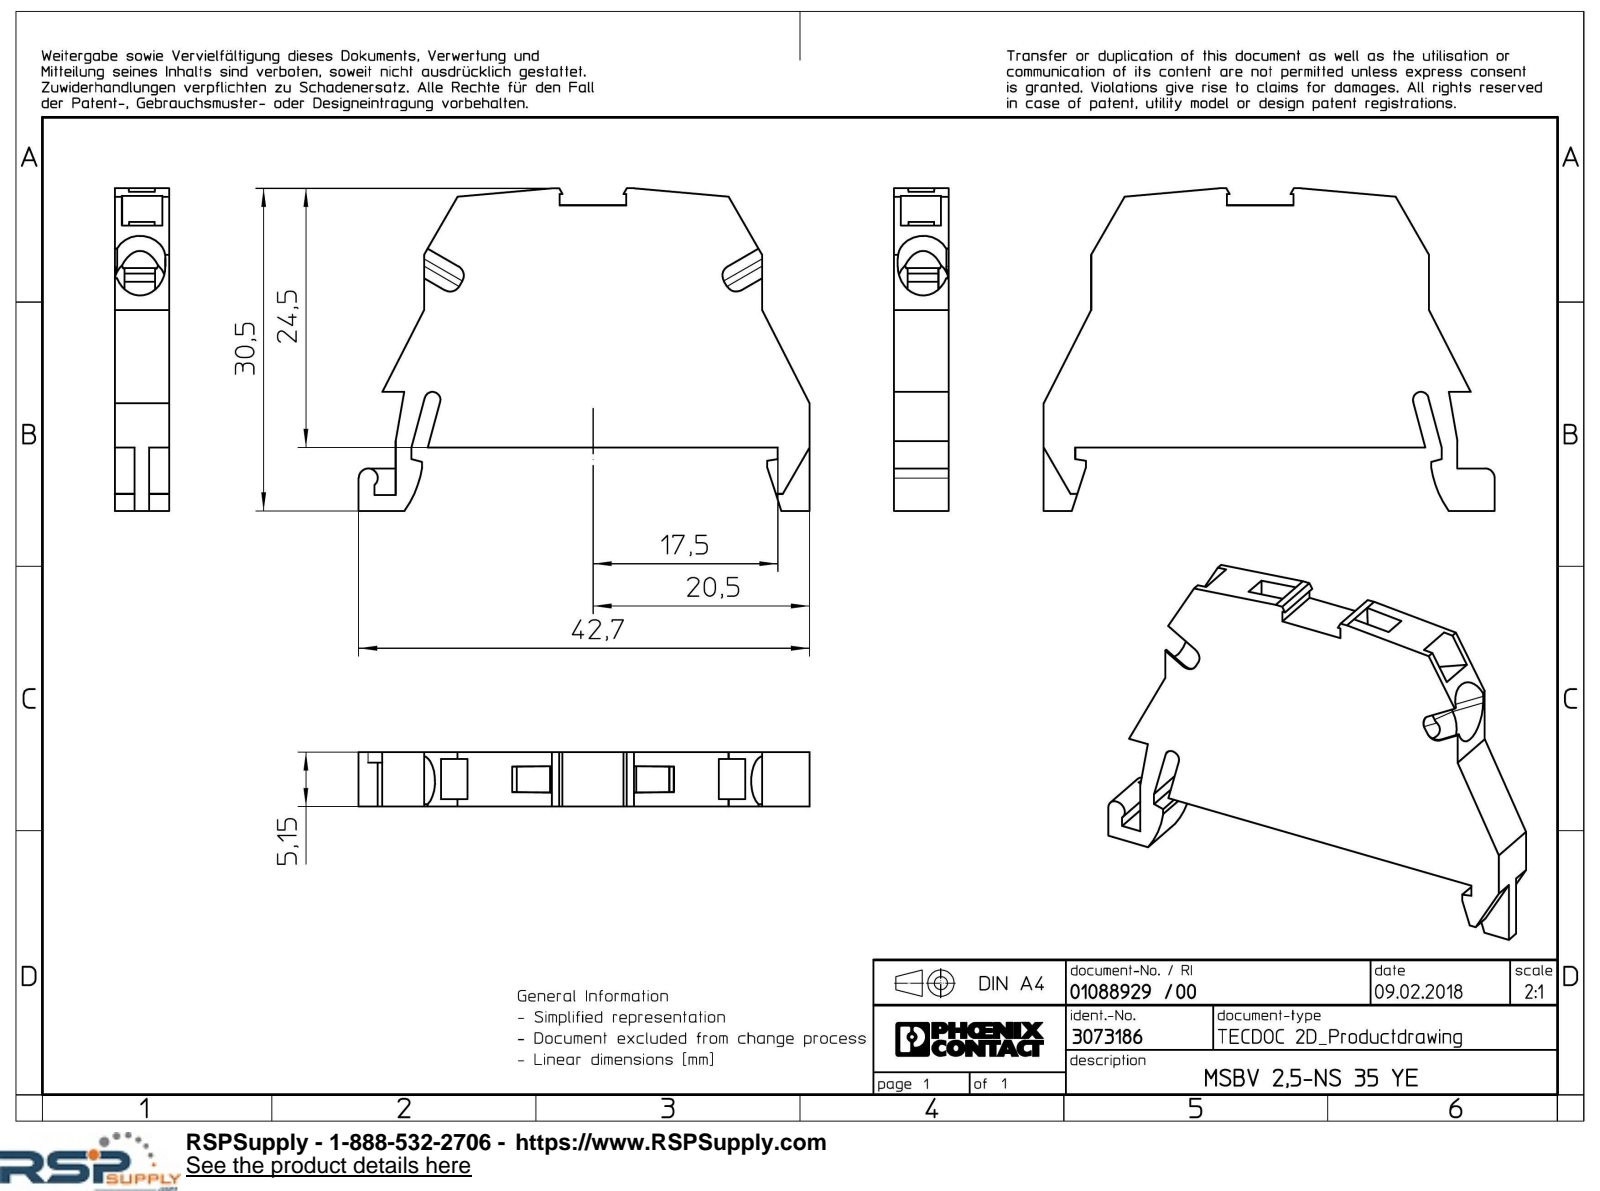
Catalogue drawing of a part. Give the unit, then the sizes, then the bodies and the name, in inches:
Units: inches
Overall size (bounding box): 1.681 × 1.201 × 0.203
Partial cylindrical surfaces — rounded edges, fillets, slot ends (radius × count): R0.039 ×8, R0.094 ×4, R0.03 ×1, R0.035 ×1, R0.374 ×1
Main face-to-face distances: 0.203, 0.026, 0.177, 0.175, 0.15, 0.028, 0.249, 0.037, 0.059, 0.114
Volume: 0.224 in³ · Surface area: 4.957 in²
Bodies: 1 solid, 125 faces (104 planar, 15 cylindrical, 6 other)
Part name (STEP PRODUCT): MSBV_2.5_NS_35_YE-select
STEP written by: Creo Elements/Direct Modeling 18.1I 14-Aug-2016 (C) Parametric Technology GmbH (AUTOMOTIVE_DESIGN)
